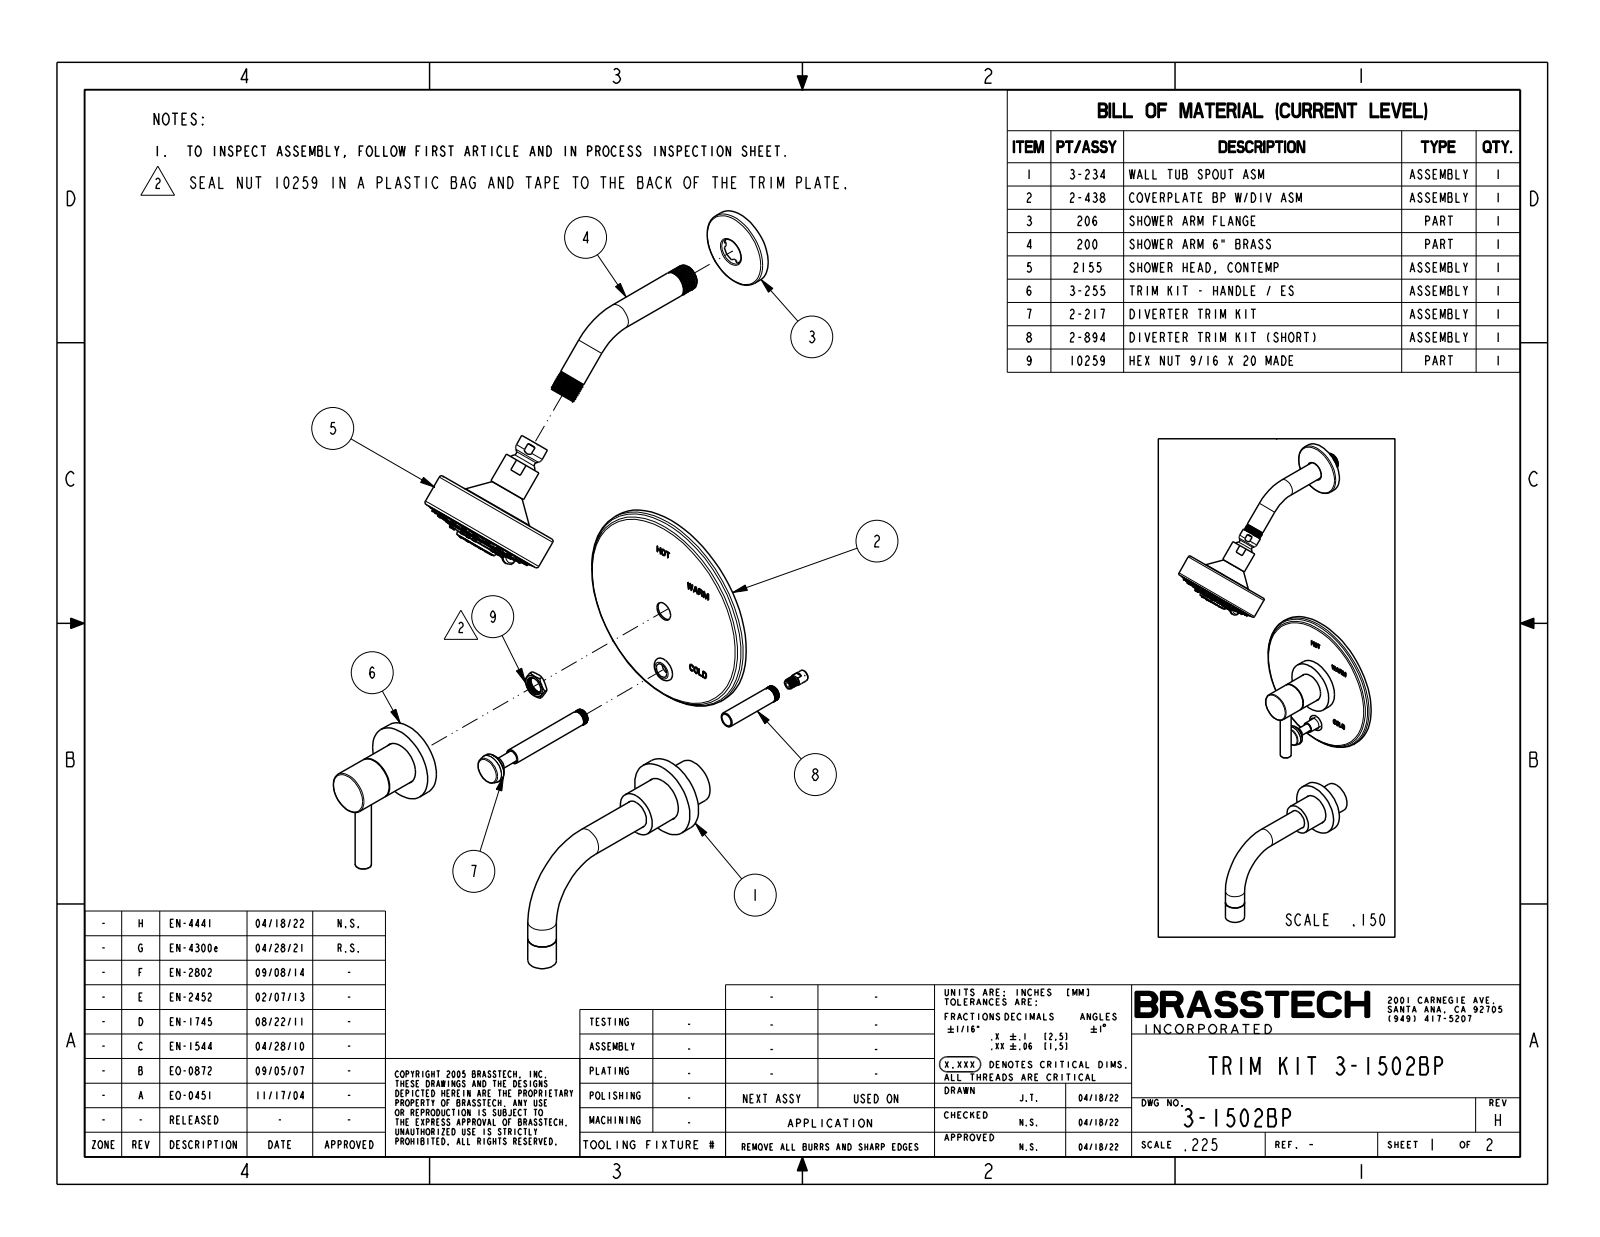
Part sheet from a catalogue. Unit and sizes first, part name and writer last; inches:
Units: inches
Overall size (bounding box): 23.63 × 8.175 × 6.5
Round holes (diameter × count): ⌀0.059 ×8, ⌀0.52 ×1, ⌀0.925 ×1
Round bosses / shafts (diameter × count): ⌀0.142 ×39, ⌀0.165 ×23, ⌀2.375 ×2, ⌀0.875 ×2, ⌀0.813 ×2, ⌀6.5 ×1, ⌀4 ×1, ⌀3.724 ×1
Partial cylindrical surfaces — rounded edges, fillets, slot ends (radius × count): R0.079 ×8, R0.02 ×2, R0.138 ×1, R0.472 ×1, R0.512 ×1, R0.63 ×1
Main face-to-face distances: 0.313, 0.062, 0.688, 0.375, 0.375, 0.313, 2.936, 2.623, 2.561, 2.248
Hole centre spacings: 0.443, 0.579, 0.818, 0.819, 1.069, 0.443, 0.578, 1.069
Volume: 45.03 in³ · Surface area: 205.6 in²
Bodies: 3 solids, 1368 faces (405 planar, 218 cylindrical, 745 other)
Part name (STEP PRODUCT): 3-1502BP
STEP written by: CREO PARAMETRIC BY PTC INC, 2018400 (CONFIG_CONTROL_DESIGN)
